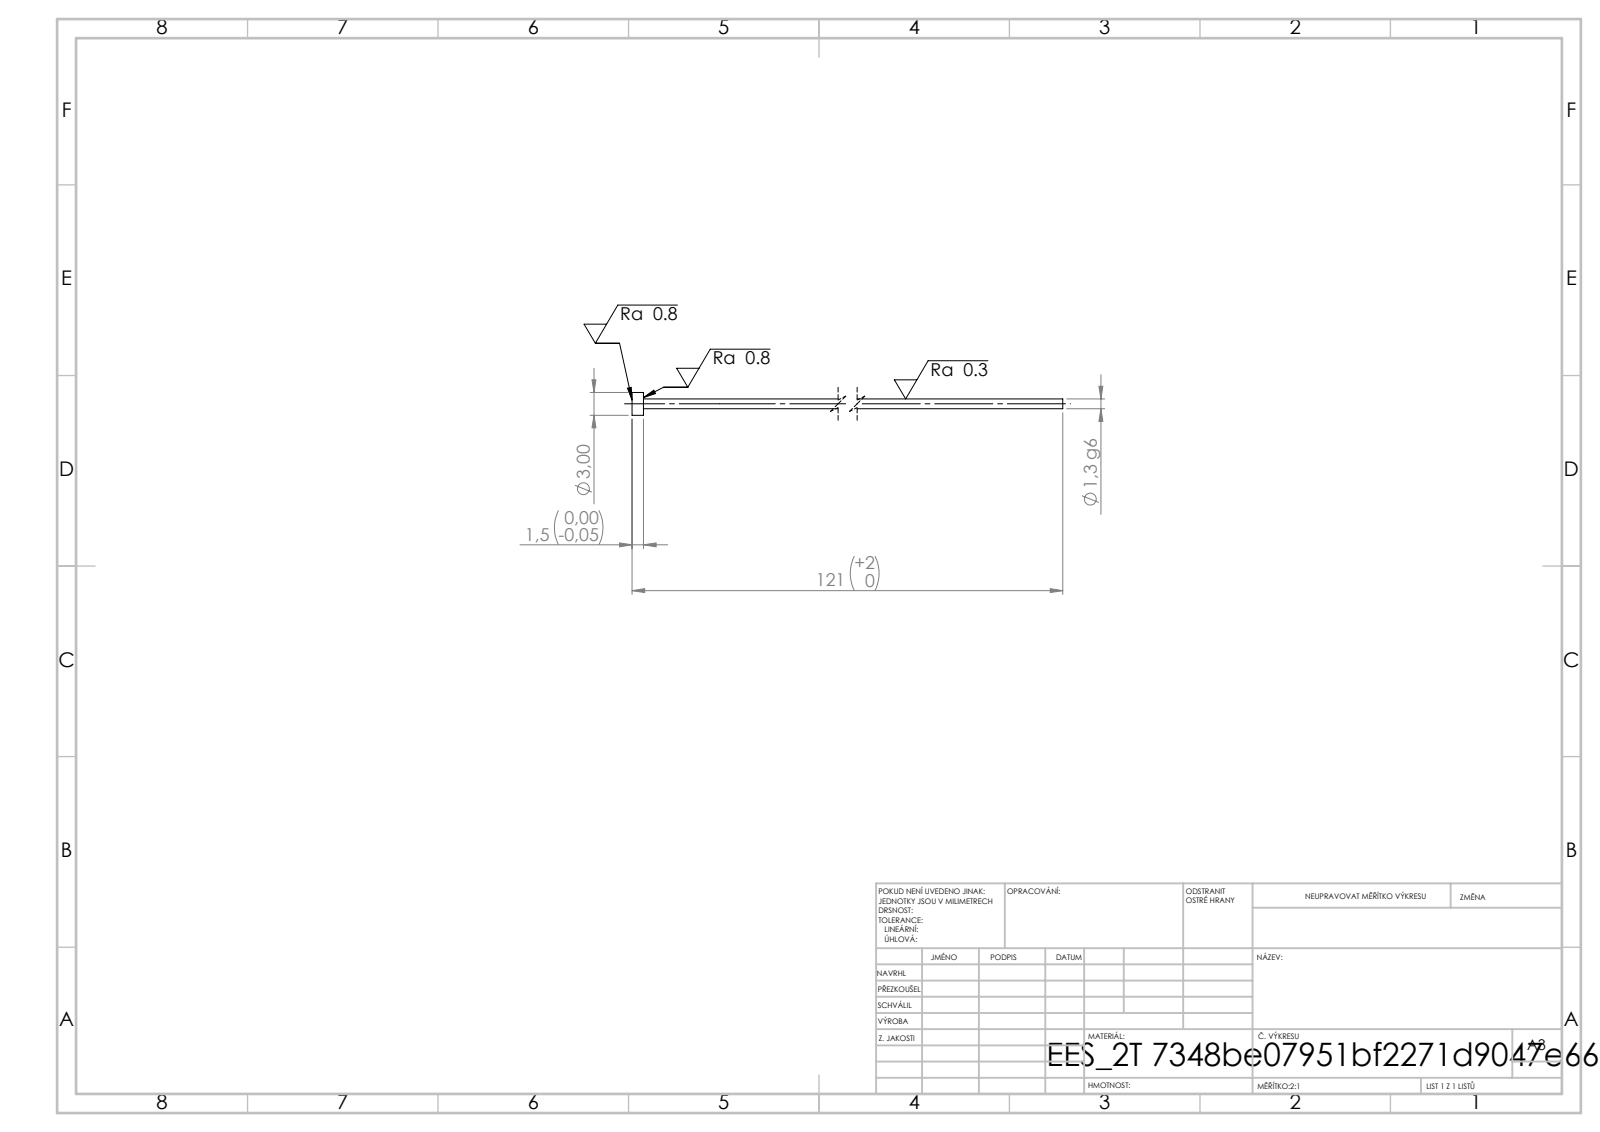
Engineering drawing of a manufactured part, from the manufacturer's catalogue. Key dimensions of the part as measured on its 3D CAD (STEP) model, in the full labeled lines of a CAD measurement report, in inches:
STEP written by: SolidWorks 2019 (CONFIG_CONTROL_DESIGN)
Units: inches
Bodies: 1 solid, 7 faces (3 planar, 4 cylindrical, 0 other)
Overall size (bounding box): 4.744 × 0.118 × 0.118
Volume: 0.01 in³ · Surface area: 0.797 in²
Round bosses / shafts (diameter × count): ⌀0.118 ×1, ⌀0.051 ×1
Main face-to-face distances: 0.059, 4.744, 4.685
